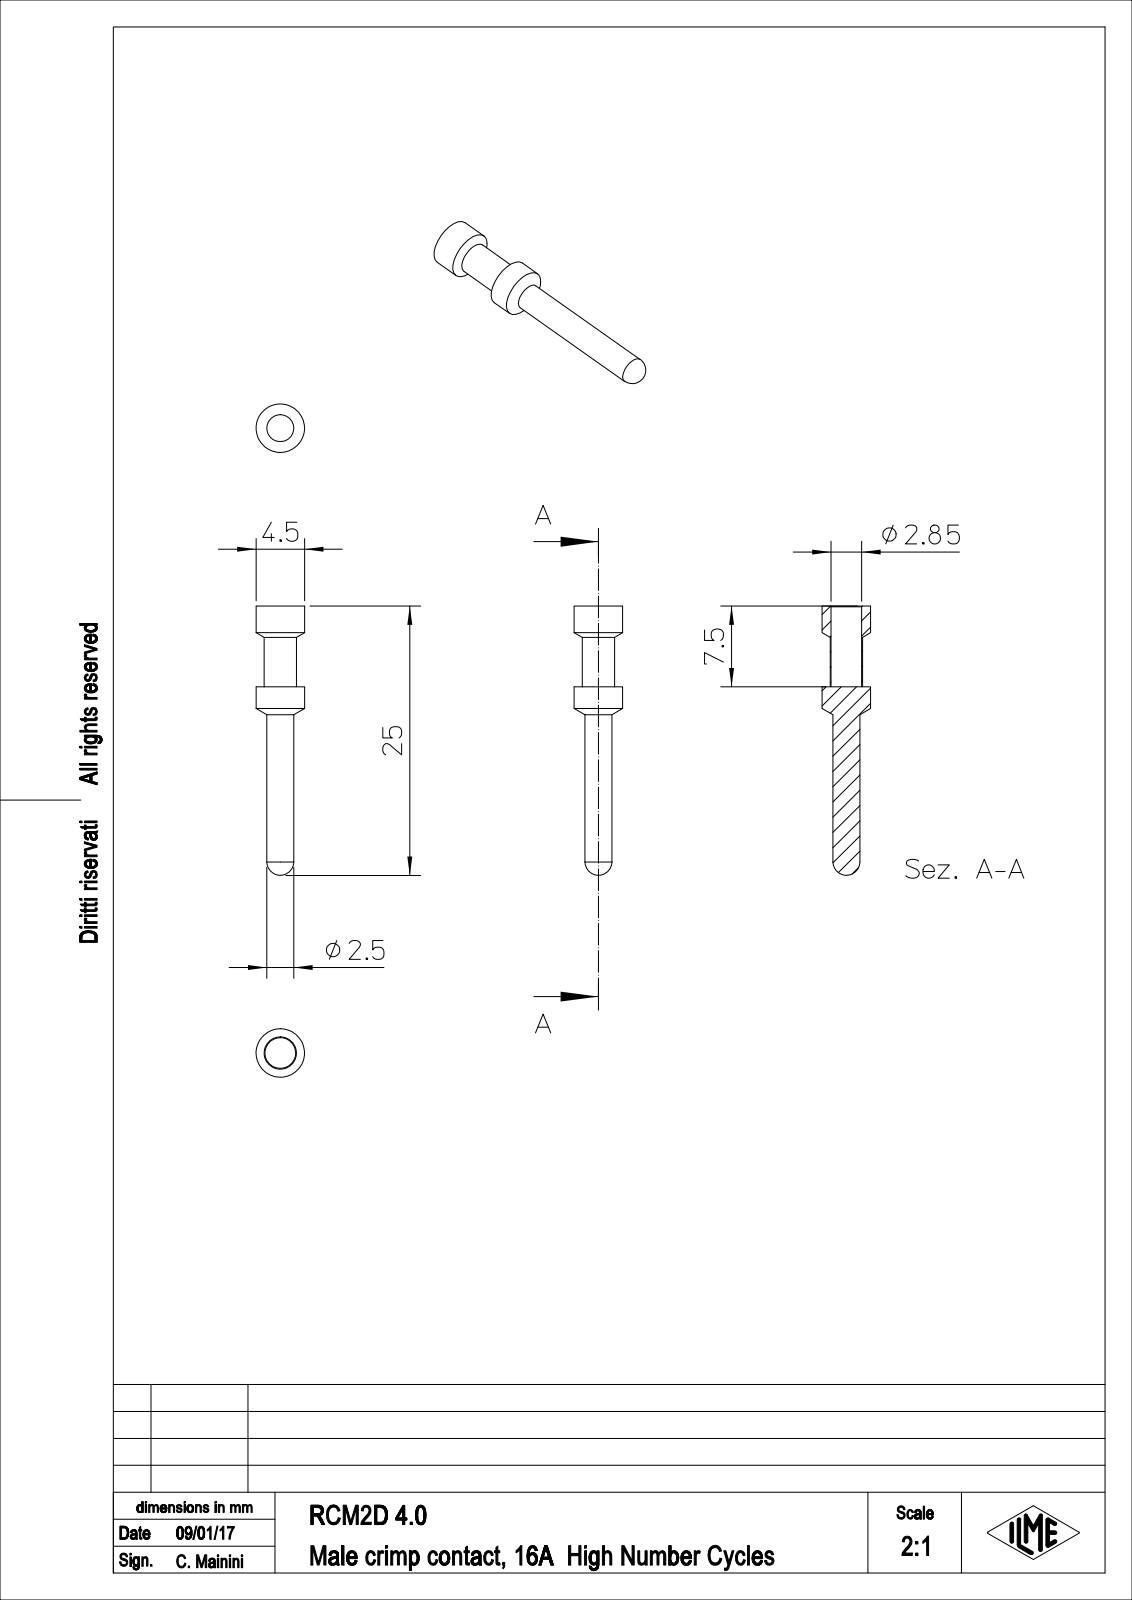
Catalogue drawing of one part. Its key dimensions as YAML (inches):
part_name: "RCM2D_4.0"
step_written_by: "PTC Creo Elements/Direct Modeling 19.0E 27-Jun-2016 (C) Parametric Technology GmbH (AUTOMOTIVE_DESIGN)"
units: inches
bodies: {solids: 1, faces: 21, planar: 3, cylindrical: 10, other: 8}
overall_size: [0.984, 0.177, 0.177]
volume: 0.008
surface_area: 0.524
round_holes:
  - {diameter: 0.112, count: 1}
round_bosses_or_shafts:
  - {diameter: 0.177, count: 1}
  - {diameter: 0.118, count: 1}
  - {diameter: 0.098, count: 1}
face_to_face_distances: [0.295]
